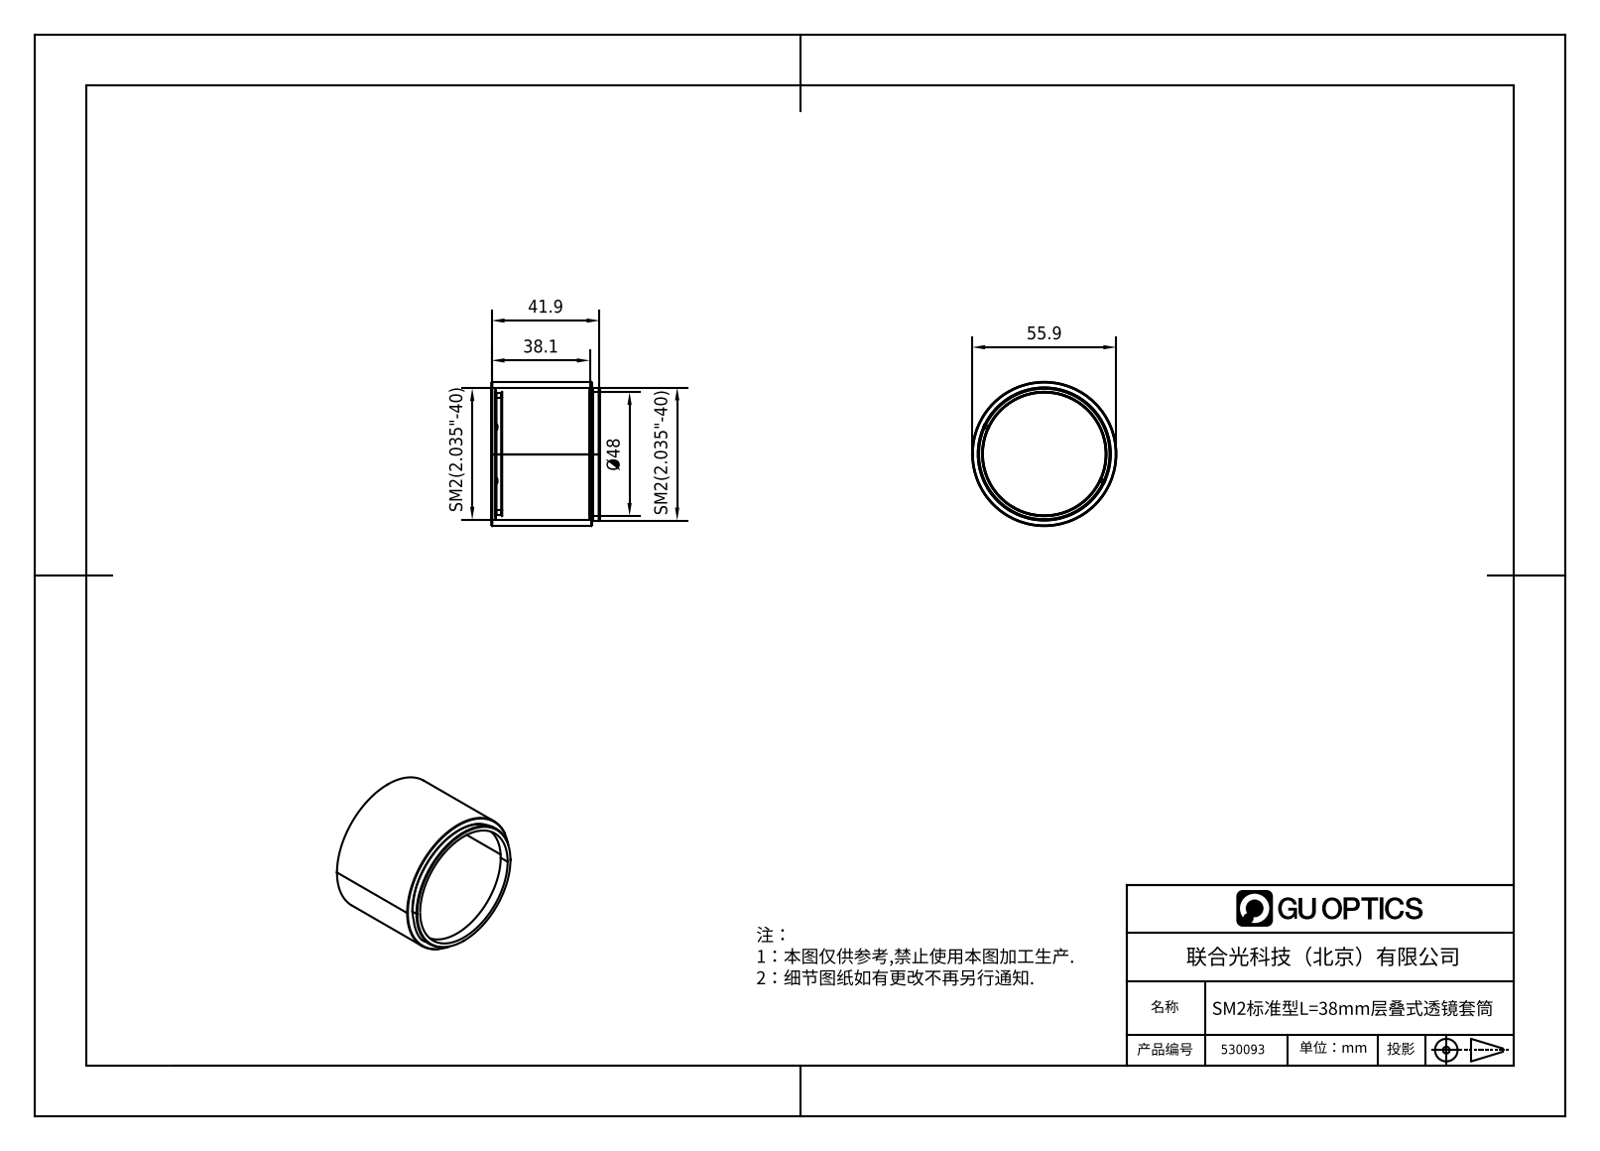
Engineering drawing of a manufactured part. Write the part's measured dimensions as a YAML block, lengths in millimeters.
part_name: "1.7.1.19_ZTC-2-1.5_SM2标准型1.5英寸层叠式透镜套筒"
step_written_by: "SolidWorks 2018 (AUTOMOTIVE_DESIGN)"
units: millimeters
bodies: {solids: 0, faces: 34, planar: 11, cylindrical: 12, other: 11}
overall_size: [55.9, 55.9, 41.9]
round_holes:
  - {diameter: 47.69, count: 1}
  - {diameter: 48, count: 1}
  - {diameter: 51.05, count: 1}
round_bosses_or_shafts:
  - {diameter: 55.9, count: 1}
  - {diameter: 51.6, count: 1}
  - {diameter: 50.6, count: 1}
face_to_face_distances: [38.9, 41.9, 3, 1.54, 37.36, 40.36, 2.24, 0.7, 36.66, 39.66]
